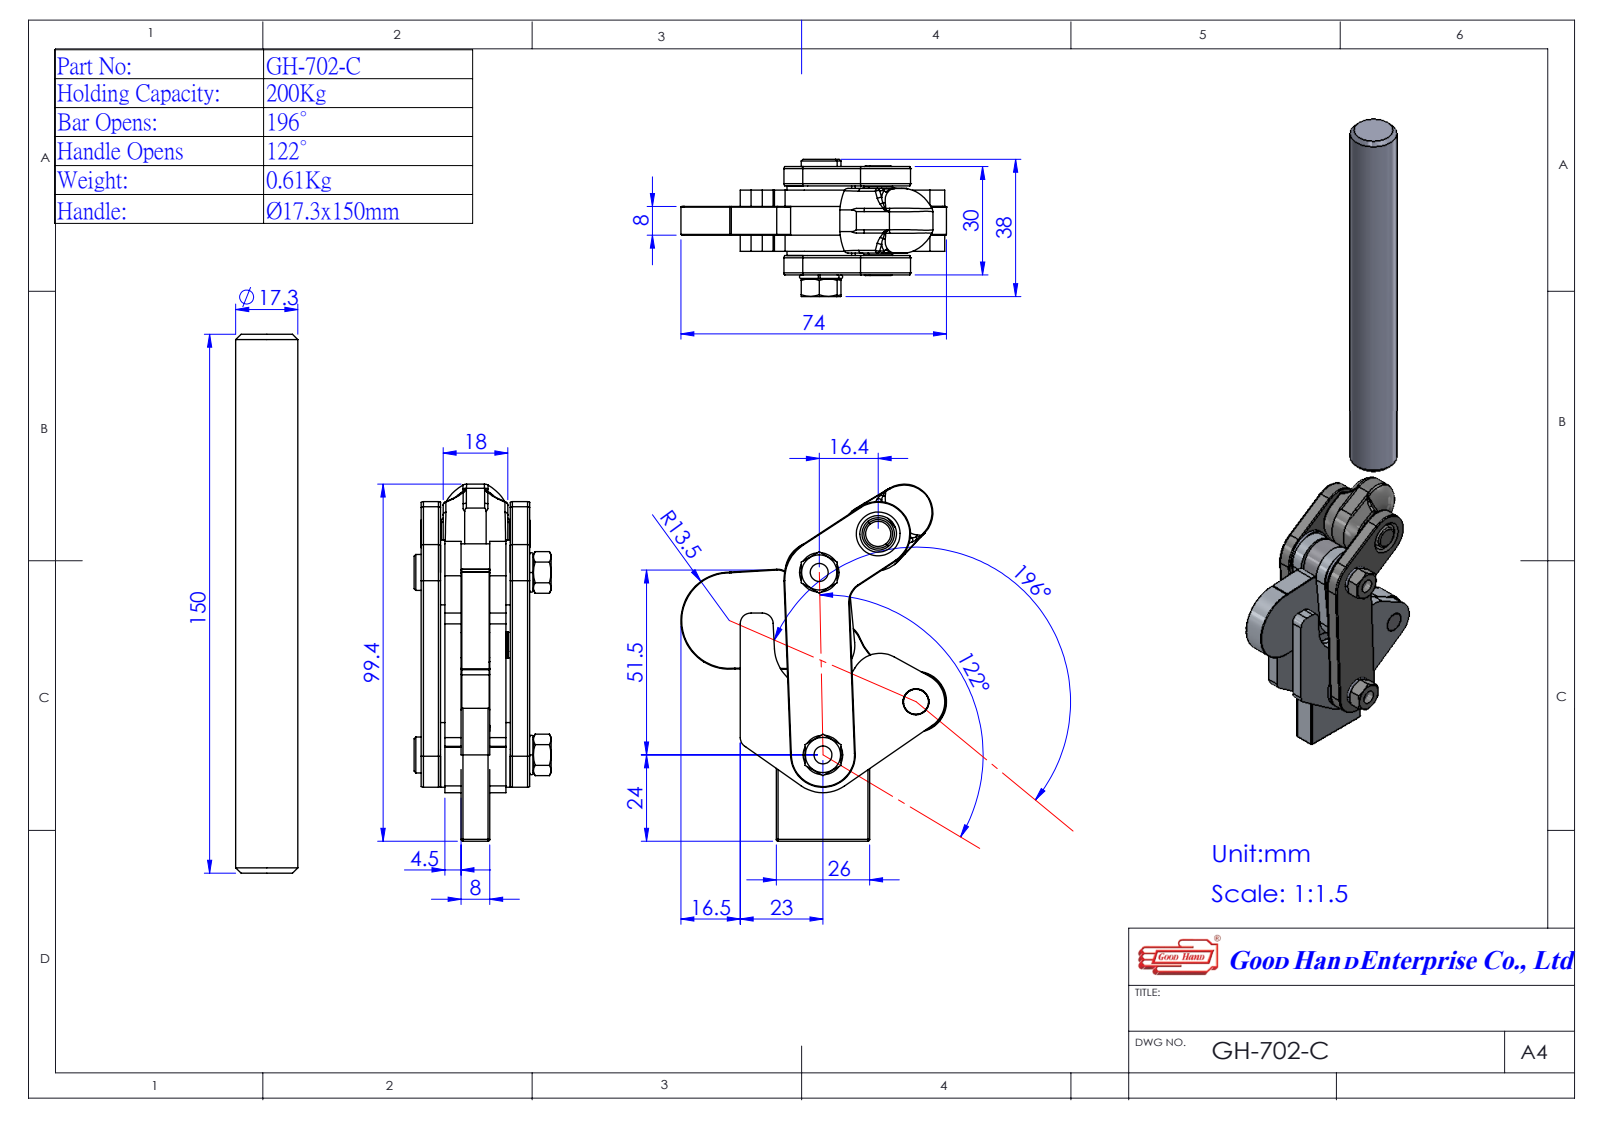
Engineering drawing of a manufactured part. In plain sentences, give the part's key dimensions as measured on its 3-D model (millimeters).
The part is named "Group6^GH-702-C(簡化版)-1; Group5^GH-702-C(簡化版)-1; 3700126-1^GH-702-C(簡化版)-1; 3700108-1^GH-702-C(簡化版)-1 (+4 more)". Its 3-D file was written by "SolidWorks 2016 (AUTOMOTIVE_DESIGN)". It is 7 solids with 289 faces: 99 planar, 136 cylindrical and 54 other. Overall it measures 251.11 by 73.95 by 38.2 millimeters. Its volume is 78 027 cubic millimeters and its surface area 46 220 square millimeters. Round holes: 4 of diameter 7, 3 of diameter 8, 2 of diameter 5, 1 of diameter 13.9. Round bosses or shafts: 4 of diameter 6.97, 2 of diameter 18, 2 of diameter 10, 1 of diameter 17.3, 1 of diameter 15.9. Partial cylindrical surfaces (rounded edges, fillets, slot ends): 16 of radius 2, 3 of radius 3, 3 of radius 8, 2 of radius 8.5, 2 of radius 8.75, 2 of radius 9.5, 1 of radius 4, 1 of radius 5.5. The main face-to-face distances are 8, 4.5, 12.5, 1.2, 5.7, 13.7, 18.2, 5.4, 6.6, 11.1. The hole center spacings are 19.61, 20.29, 29.83, 30.2, 30.53, 34.54, 44.96, 47.89.
